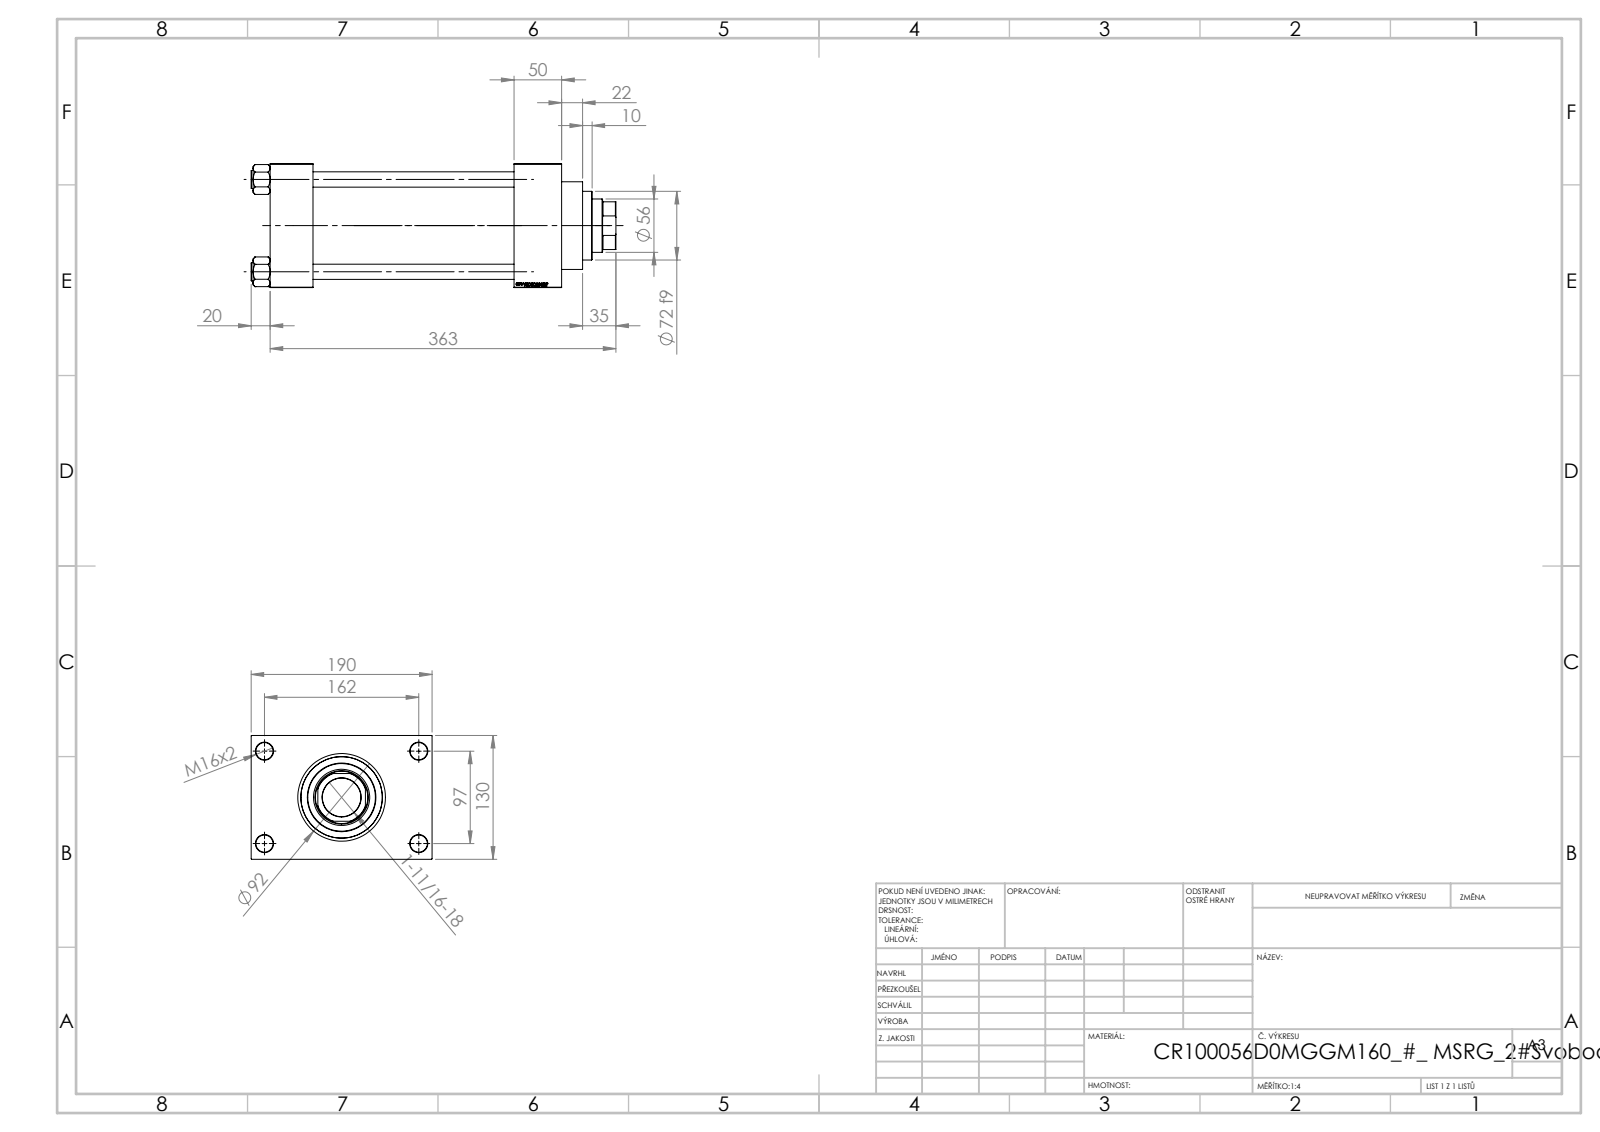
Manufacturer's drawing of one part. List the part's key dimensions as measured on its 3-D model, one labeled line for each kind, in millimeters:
Part name (STEP PRODUCT): V215CR_VCP_D; V215CR_D_Body; V215_VC_A; NUT_M5_D (+1 more)
STEP written by: SolidWorks 2019 (CONFIG_CONTROL_DESIGN)
Units: millimetres
Bodies: 11 solids, 1152 faces (545 planar, 89 cylindrical, 518 other)
Overall size (bounding box): 383 × 190 × 130
Volume: 3 238 000 mm³ · Surface area: 503 262 mm²
Round holes (diameter × count): ⌀16 ×4, ⌀18 ×4, ⌀7 ×2, ⌀26.44 ×2, ⌀35 ×2, ⌀40.5 ×1, ⌀56 ×1, ⌀59 ×1, ⌀76 ×1, ⌀85.5 ×1, ⌀100 ×1
Round bosses / shafts (diameter × count): ⌀19 ×4, ⌀106 ×1, ⌀92 ×1, ⌀72 ×1
Partial cylindrical surfaces — rounded edges, fillets, slot ends (radius × count): R27 ×1
Main face-to-face distances: 130, 50, 45, 256, 211, 160, 306, 261, 30, 190
Hole centre spacings: 32.55, 68.52, 94.41, 96.9, 102.27, 129.45, 161.73, 97
